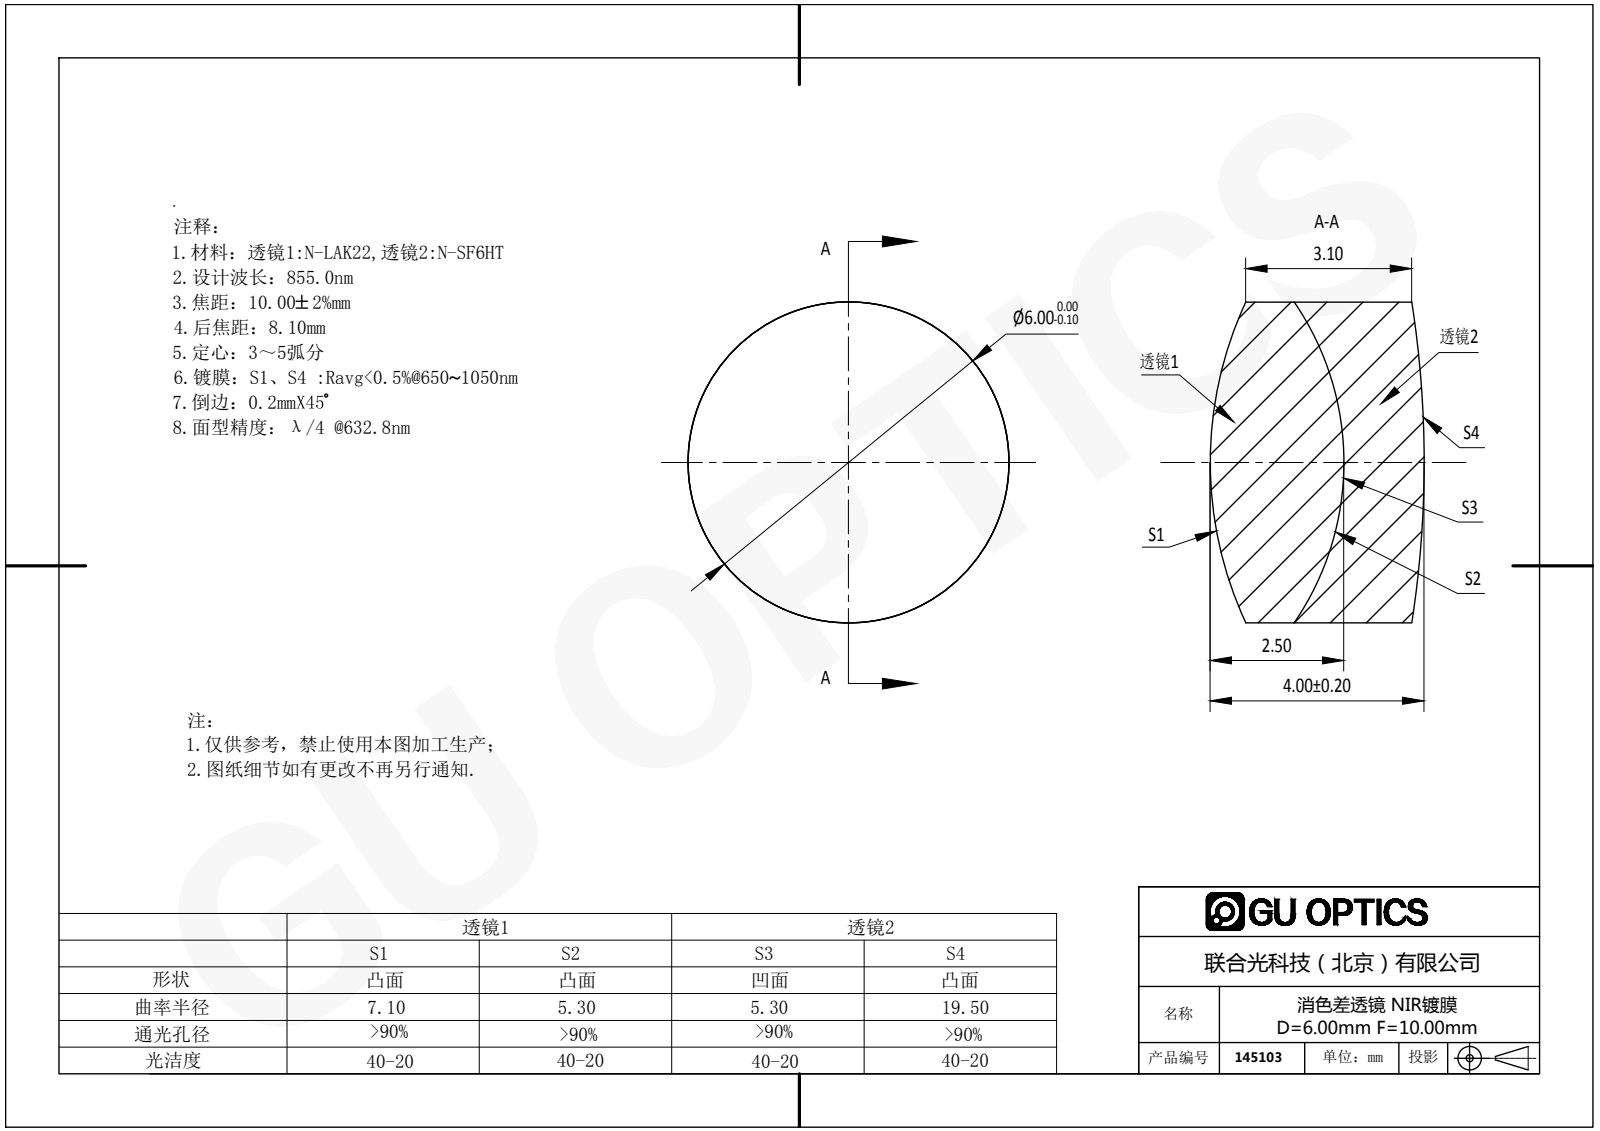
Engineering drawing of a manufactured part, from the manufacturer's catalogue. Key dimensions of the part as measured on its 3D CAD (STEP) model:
Part name (STEP PRODUCT): 145103
STEP written by: SolidWorks 2016 (AUTOMOTIVE_DESIGN)
Units: millimetres
Bodies: 2 solids, 12 faces (0 planar, 4 cylindrical, 8 other)
Overall size (bounding box): 6 × 6 × 4
Volume: 101 mm³ · Surface area: 179 mm²
Round bosses / shafts (diameter × count): ⌀6 ×1
